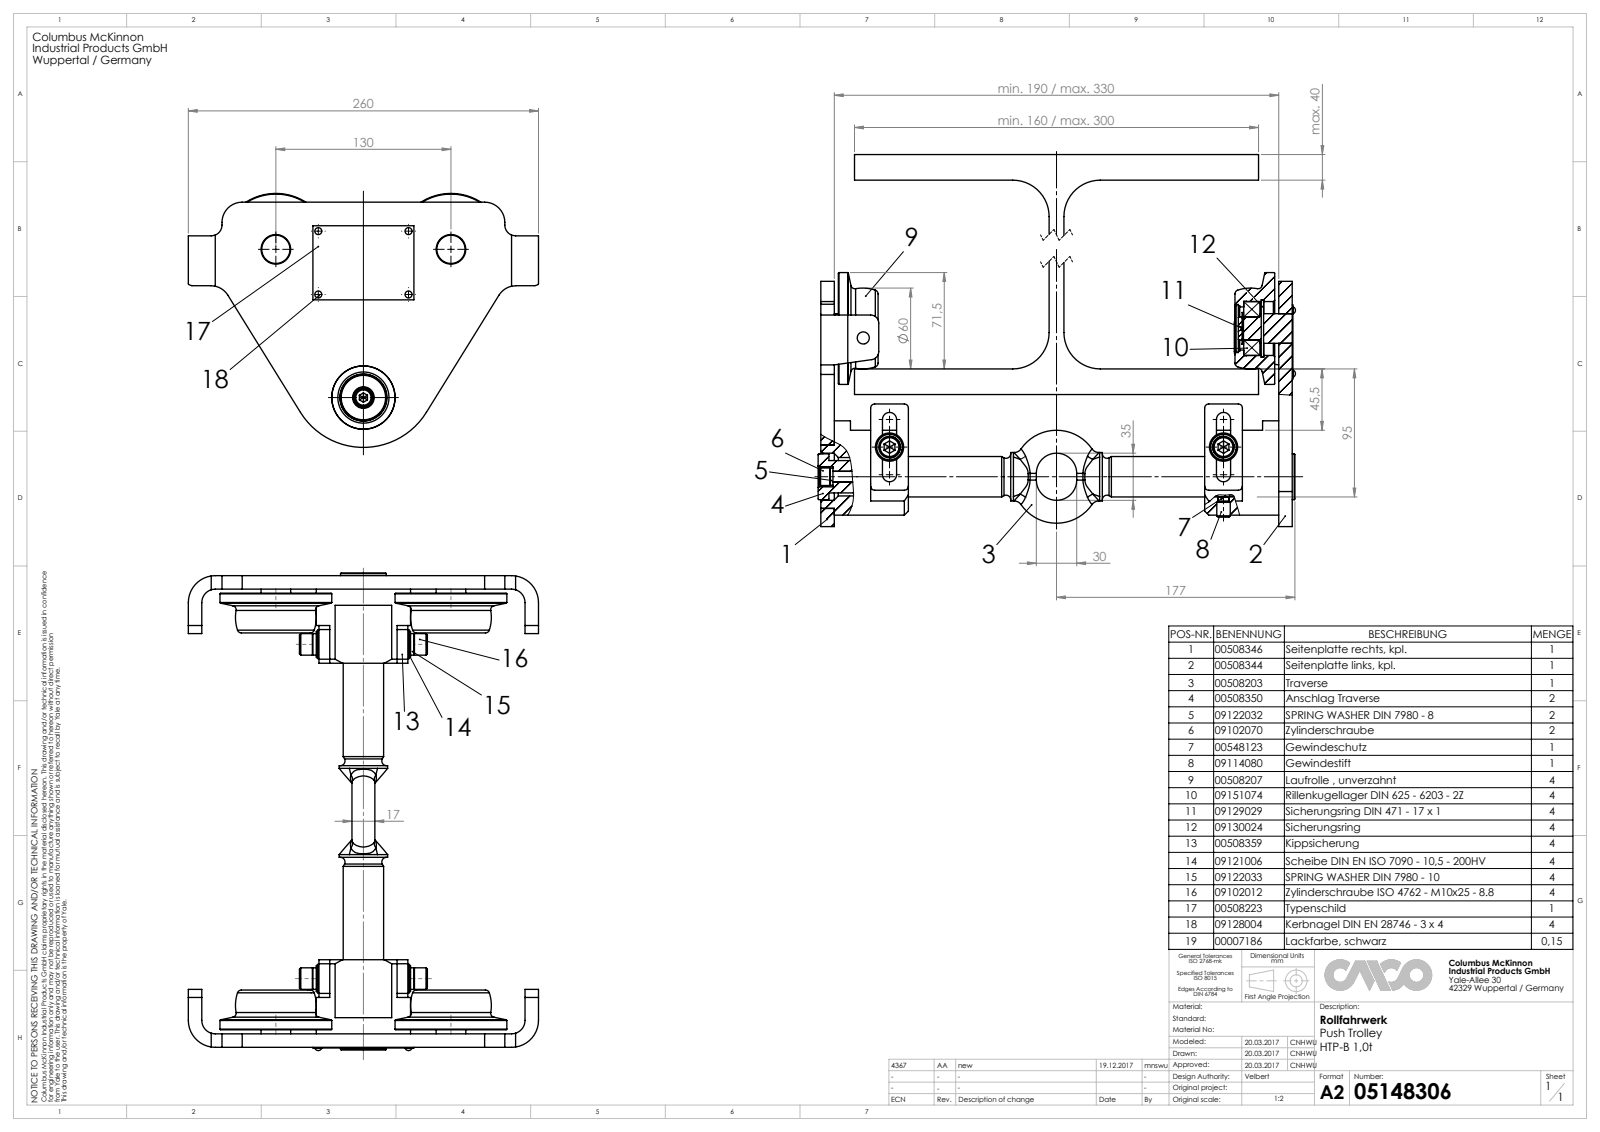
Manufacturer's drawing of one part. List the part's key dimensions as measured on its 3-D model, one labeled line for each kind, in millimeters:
Part name (STEP PRODUCT): HTP-B 1,0t
STEP written by: SolidWorks 2015 (AUTOMOTIVE_DESIGN)
Units: millimetres
Bodies: 55 solids, 1168 faces (400 planar, 442 cylindrical, 326 other)
Overall size (bounding box): 400 × 398 × 354.4
Volume: 7 546 000 mm³ · Surface area: 1 118 000 mm²
Round holes (diameter × count): ⌀1.7 ×4, ⌀2.5 ×4, ⌀3 ×4, ⌀3.5 ×4, ⌀8.5 ×3, ⌀2 ×2, ⌀9 ×2, ⌀10.2 ×2, ⌀10.5 ×2, ⌀16.2 ×2, ⌀22 ×2, ⌀30.91 ×2
Round bosses / shafts (diameter × count): ⌀16 ×4, ⌀5.2 ×4, ⌀10 ×3, ⌀83 ×2, ⌀42.5 ×2, ⌀23.79 ×2, ⌀21 ×2, ⌀17 ×2
Partial cylindrical surfaces — rounded edges, fillets, slot ends (radius × count): R3 ×8, R1.7 ×4, R2.5 ×4, R5.25 ×4, R6 ×4, R10 ×4, R15 ×4, R20 ×4
Main face-to-face distances: 19, 281, 300, 262, 11, 10, 169.5, 180.5, 159.5, 170.5
Hole centre spacings: 130, 8.38, 9.84, 9.99, 18.35, 4.25, 6.25, 34.27
